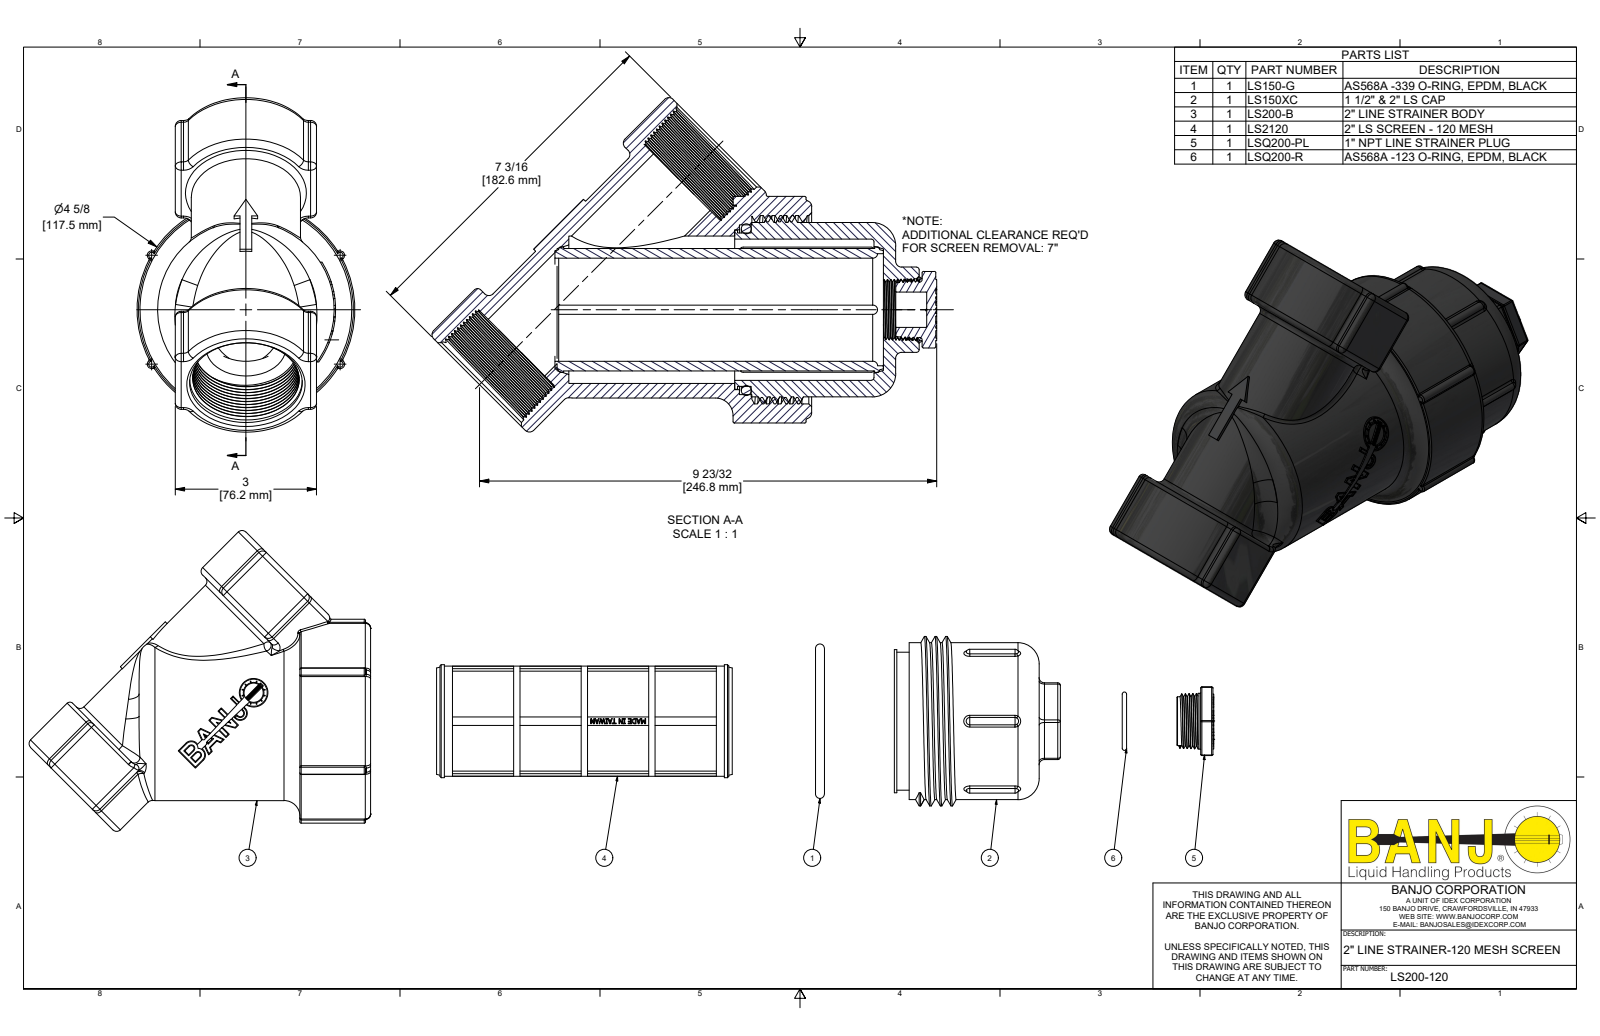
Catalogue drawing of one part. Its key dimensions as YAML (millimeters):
part_name: "LS200-120; LS200-B; LS150-C; LS150XC (+4 more)"
step_written_by: "Autodesk Inventor 2022 (AUTOMOTIVE_DESIGN)"
units: millimeters
bodies: {solids: 6, faces: 1766, planar: 867, cylindrical: 277, other: 622}
overall_size: [272.4, 180.4, 117.5]
volume: 886900
surface_area: 311400
round_holes:
  - {diameter: 43.2, count: 2}
  - {diameter: 11.5, count: 1}
  - {diameter: 16.3, count: 1}
  - {diameter: 19.1, count: 1}
  - {diameter: 55.6, count: 1}
  - {diameter: 59.7, count: 1}
  - {diameter: 76.2, count: 1}
  - {diameter: 79.5, count: 1}
  - {diameter: 86.2, count: 1}
  - {diameter: 91.6, count: 1}
  - {diameter: 94.7, count: 1}
  - {diameter: 101.6, count: 1}
round_bosses_or_shafts:
  - {diameter: 117.5, count: 1}
  - {diameter: 95.3, count: 1}
  - {diameter: 94, count: 1}
  - {diameter: 85.9, count: 1}
  - {diameter: 82.7, count: 1}
  - {diameter: 67.7, count: 1}
  - {diameter: 66, count: 1}
  - {diameter: 60.5, count: 1}
partial_cylinders:
  - {radius: 1.5, count: 46}
  - {radius: 3.2, count: 34}
  - {radius: 0.8, count: 30}
  - {radius: 2.4, count: 11}
  - {radius: 2.5, count: 4}
  - {radius: 2.3, count: 3}
  - {radius: 1.7, count: 2}
  - {radius: 2.1, count: 2}
face_to_face_distances: [34, 6.6, 76.2, 80.3, 6.4, 70.7, 36.7, 98.4, 5.1, 8.9]
